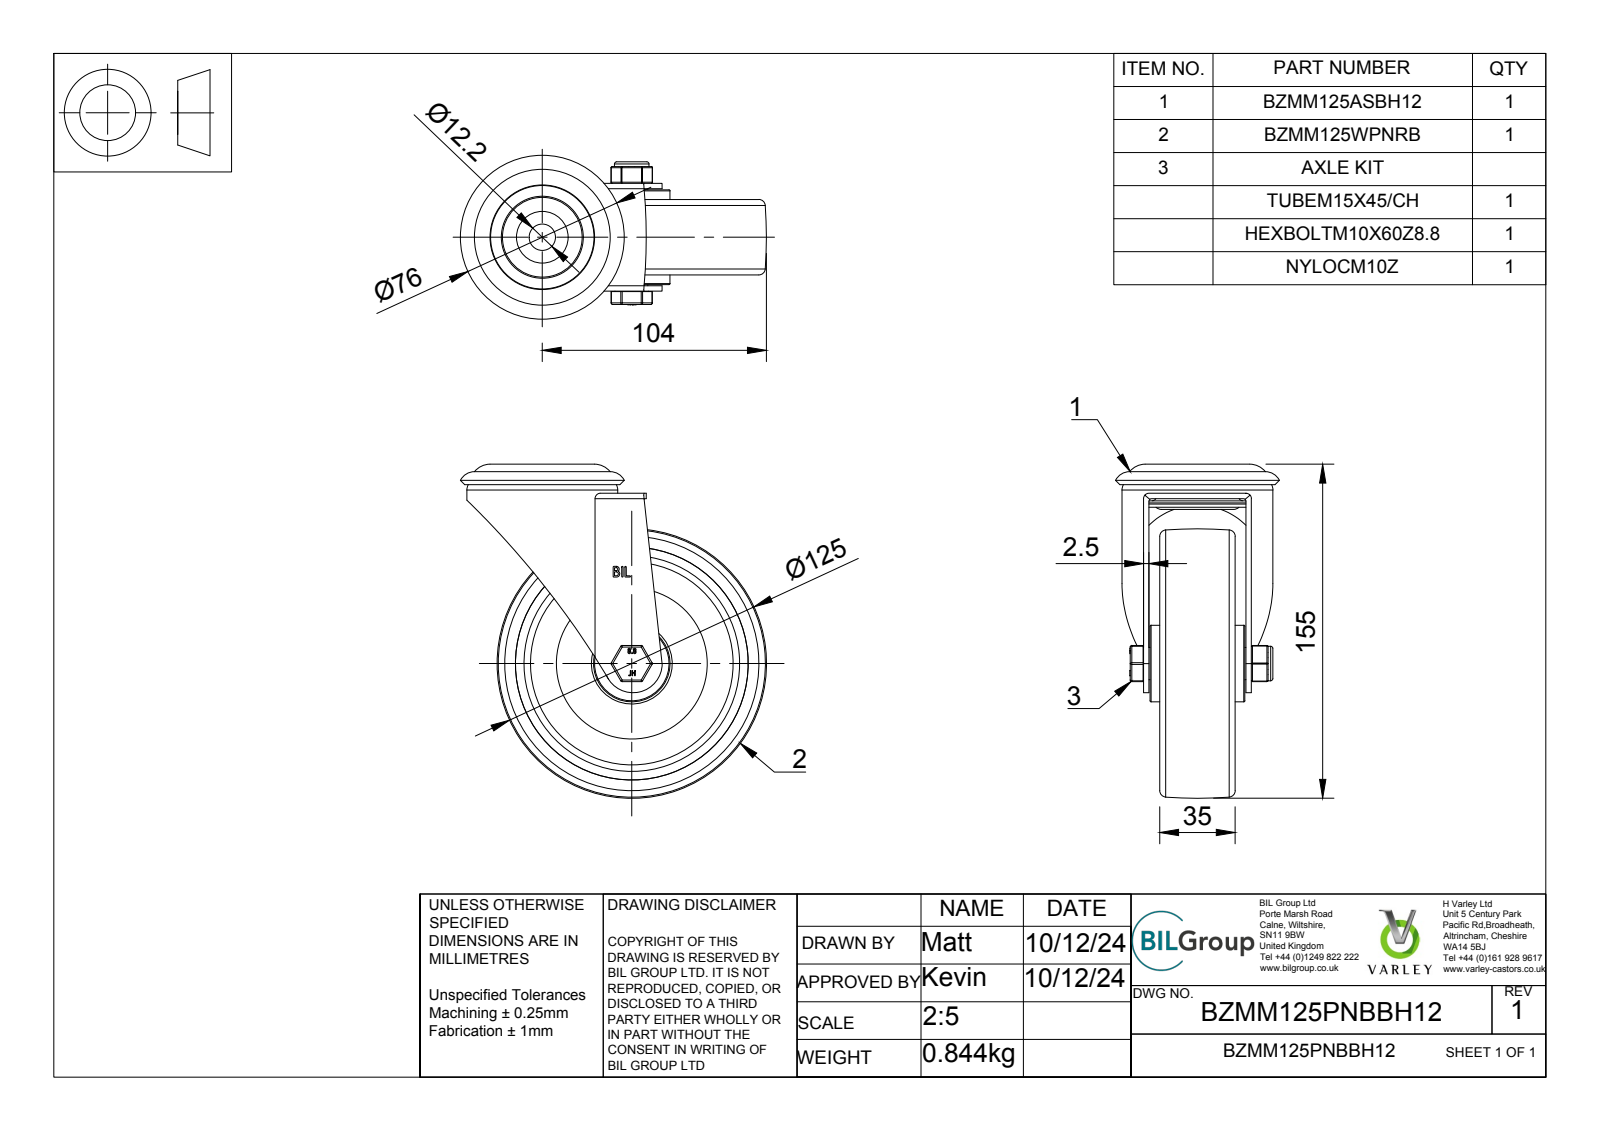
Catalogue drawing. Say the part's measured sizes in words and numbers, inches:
The part is named "BZMM125PNBBH12 v3; BZMM125ASBH12 v1; ZINC PLATED, PRESSED STEEL HEAD; ZINC PLATED, PRESSED STEEL FORKS (+8 more)". Its 3-D file was written by "Autodesk Translation Framework v13.20.0.188 (AP242_MANAGED_MODEL_BASED_3D_ENGINEERING_MIM_LF)". It is 18 solids with 437 faces: 187 planar, 141 cylindrical and 109 other. Overall it measures 6.102 by 5.591 by 2.992 inches. Its volume is 18.08 cubic inches and its surface area 219.4 square inches. Round holes: 1 of diameter 0.394, 1 of diameter 0.402, 1 of diameter 0.472, 1 of diameter 0.48, 1 of diameter 0.61, 1 of diameter 0.63, 1 of diameter 0.925, 1 of diameter 1.024, 1 of diameter 2.559, 1 of diameter 2.835, 1 of diameter 3.937, 1 of diameter 4.252. Round bosses or shafts: 8 of diameter 0.157, 1 of diameter 2.756, 1 of diameter 1.949, 1 of diameter 1.496, 1 of diameter 1.398, 1 of diameter 1.02, 1 of diameter 0.945, 1 of diameter 0.896. Partial cylindrical surfaces (rounded edges, fillets, slot ends): 18 of radius 0.02, 12 of radius 0.03, 4 of radius 0.049, 2 of radius 0.098, 1 of radius 0.379, 1 of radius 0.531, 1 of radius 9.985, 1 of radius 16.071. The main face-to-face distances are 0.778, 0.098, 0.6, 0.177, 0.797, 1.575, 0.295, 0.896, 1.073, 1.673.
